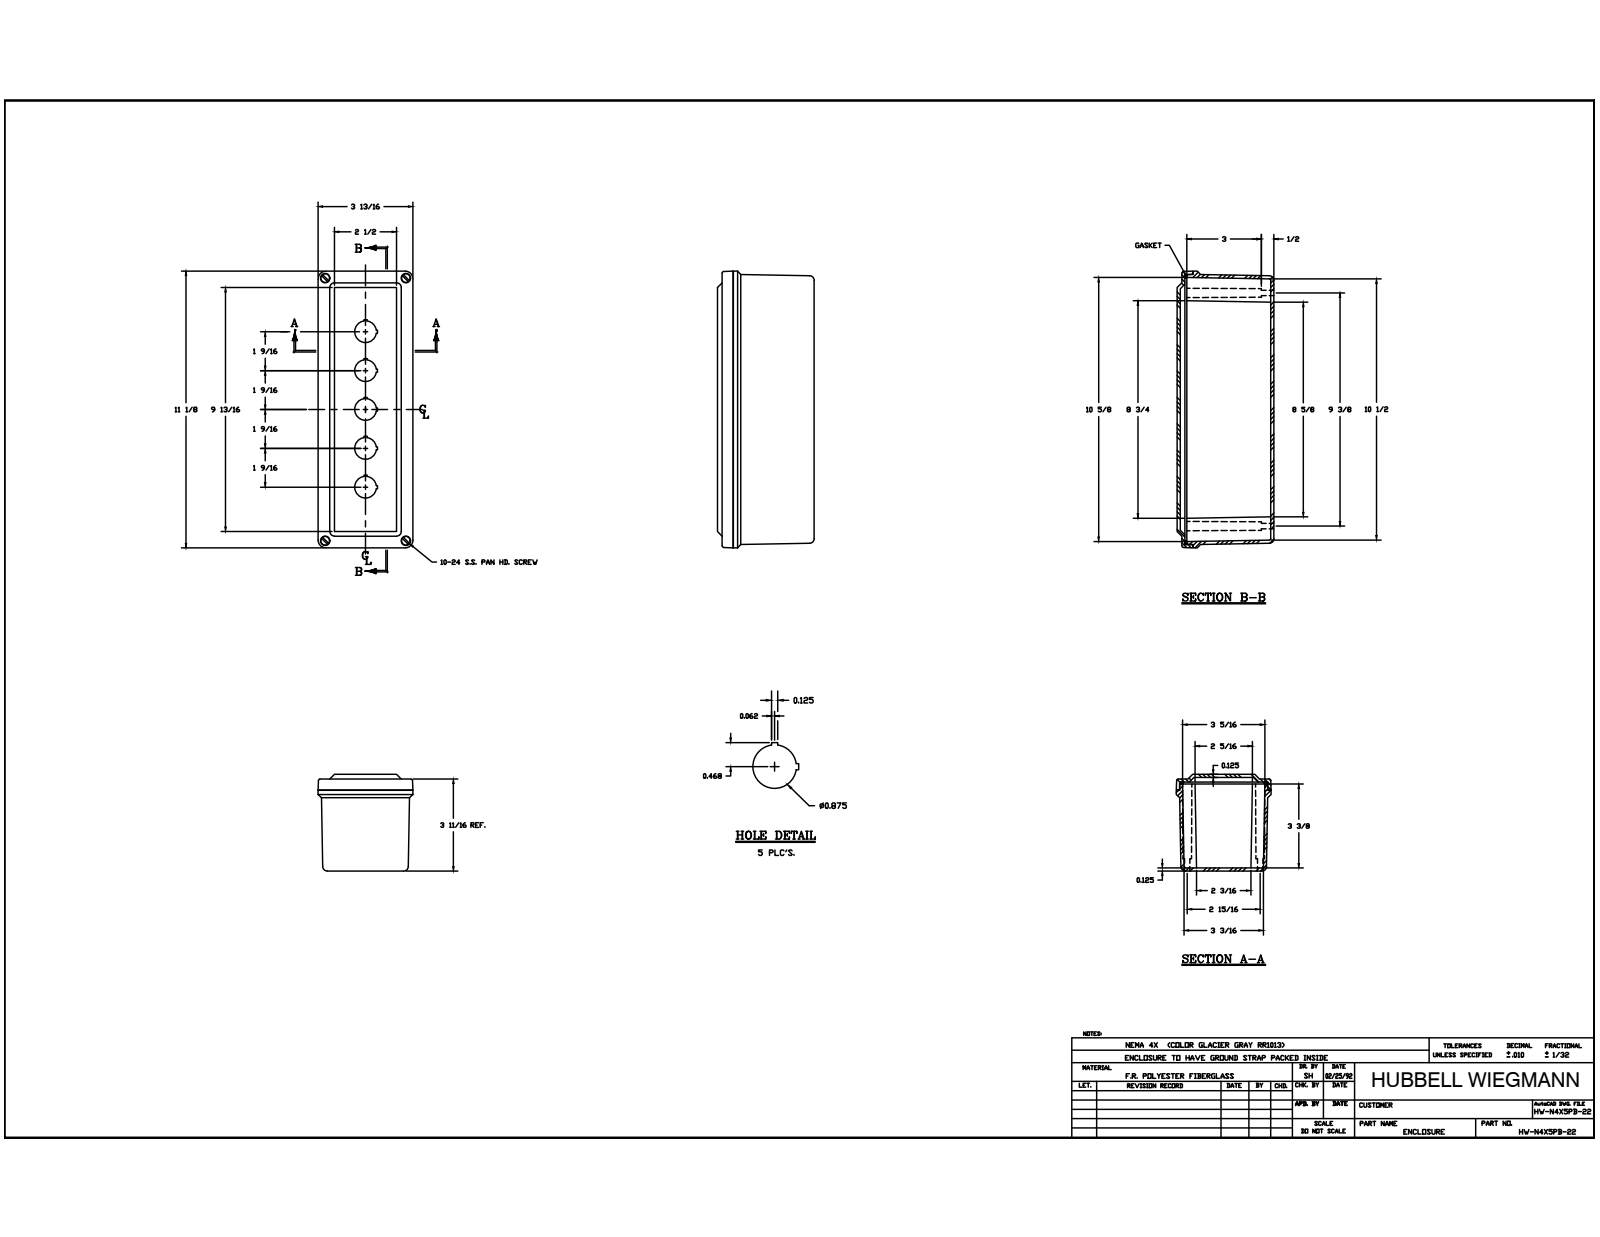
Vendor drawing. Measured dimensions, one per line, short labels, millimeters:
name: WPCF1144 BOX; 10-24 X 0.4375 DP BRASS INSERT; 10-24x0.75L combo screw; WPCF1144 GASKET (+3 more)
written by: Autodesk Inventor 2014 (AUTOMOTIVE_DESIGN)
unit: mm
bodies: 11 solids, 419 faces (213 planar, 114 cylindrical, 92 other)
size: 282.57 × 98.42 × 96.84
volume: 474 622 mm³; area: 259 531 mm²
holes: 8× ⌀5.56, 5× ⌀22.22, 4× ⌀3.68, 4× ⌀4.83, 4× ⌀9.52
bosses: 4× ⌀9.42, 4× ⌀5.54, 4× ⌀4.5
rounds: 20× R0.79, 16× R0.3, 8× R7.94, 4× R1.59, 4× R4.47, 4× R4.76, 4× R5.59, 4× R8.26
face distances: 3.17, 3.42, 95.25, 4.76, 90.49, 98.42, 92.08, 12.7, 1.59, 87.32
hole spacings: 15.59, 140.35, 178.66, 217.47, 253.23, 268.28, 39.69, 54.47
